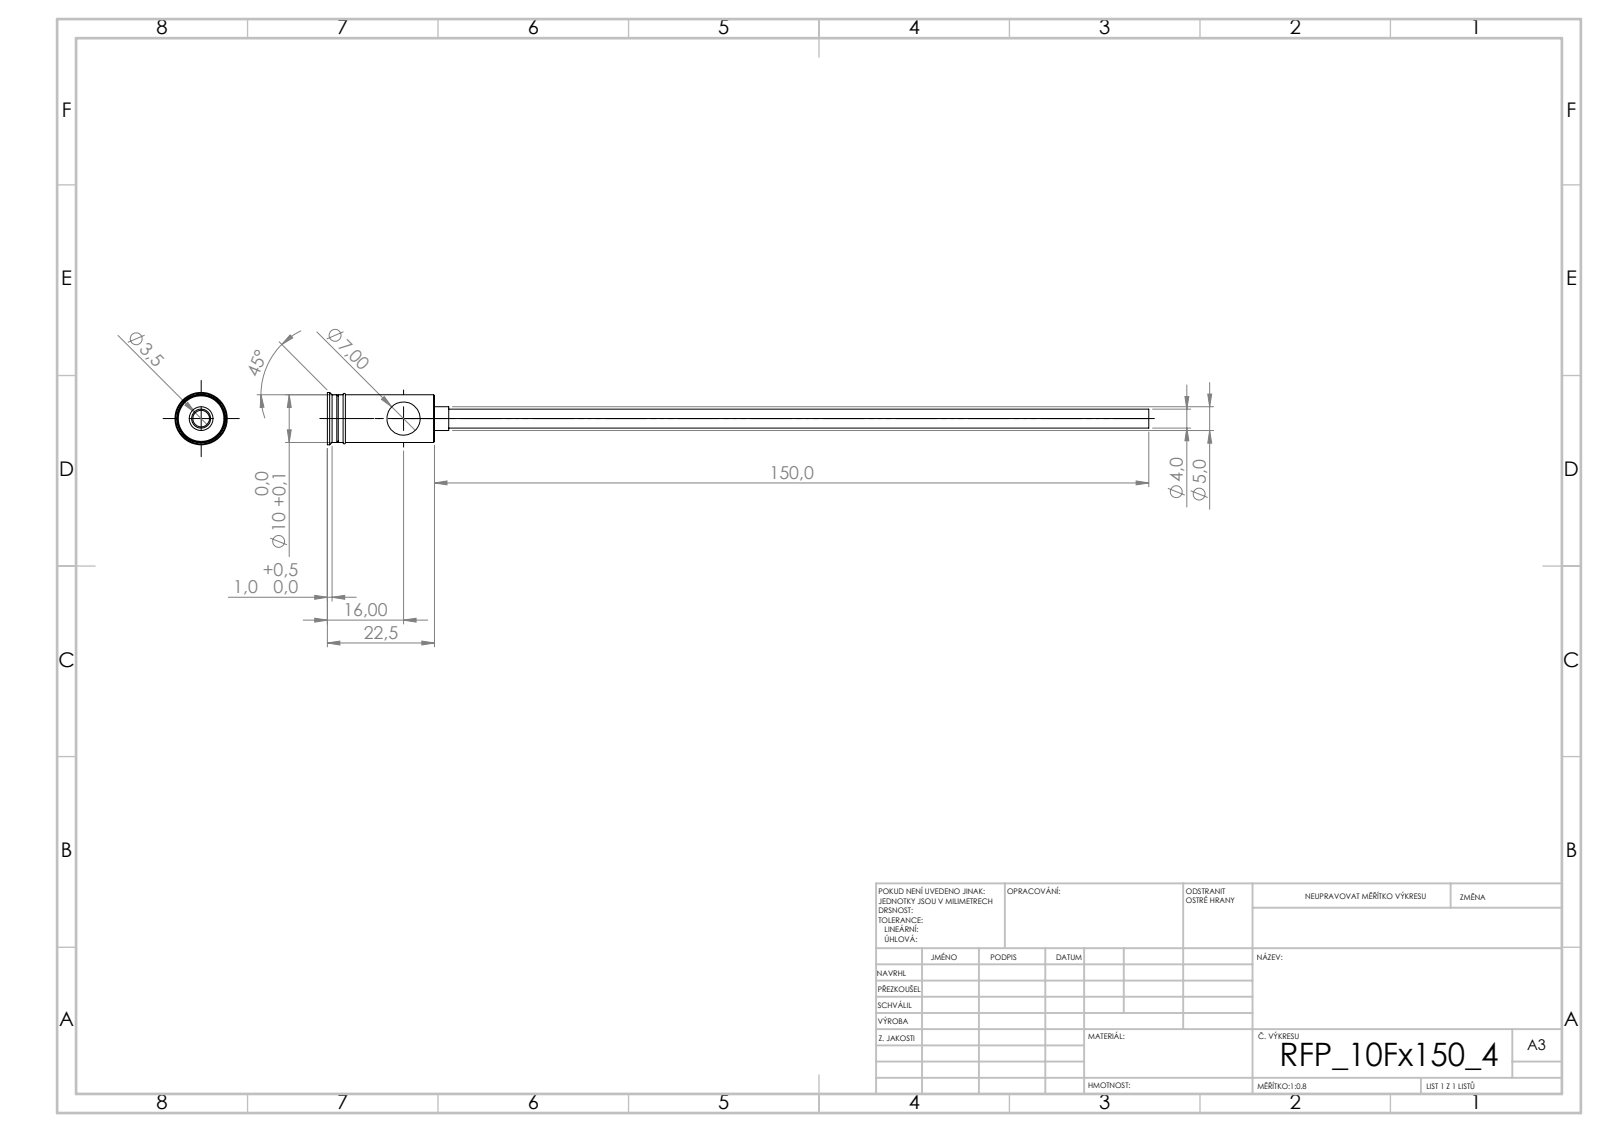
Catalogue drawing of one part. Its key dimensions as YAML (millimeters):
step_written_by: "SolidWorks 2019 (CONFIG_CONTROL_DESIGN)"
units: millimeters
bodies: {solids: 1, faces: 44, planar: 20, cylindrical: 16, other: 8}
overall_size: [172.5, 11, 11]
volume: 1804
surface_area: 4614
round_holes:
  - {diameter: 3.5, count: 1}
  - {diameter: 7, count: 1}
round_bosses_or_shafts:
  - {diameter: 11, count: 1}
  - {diameter: 10, count: 1}
  - {diameter: 5, count: 1}
  - {diameter: 4, count: 1}
face_to_face_distances: [22.5, 20.5, 2, 5.4, 20.2, 2.3, 3, 23.2, 23.5, 25.5]
